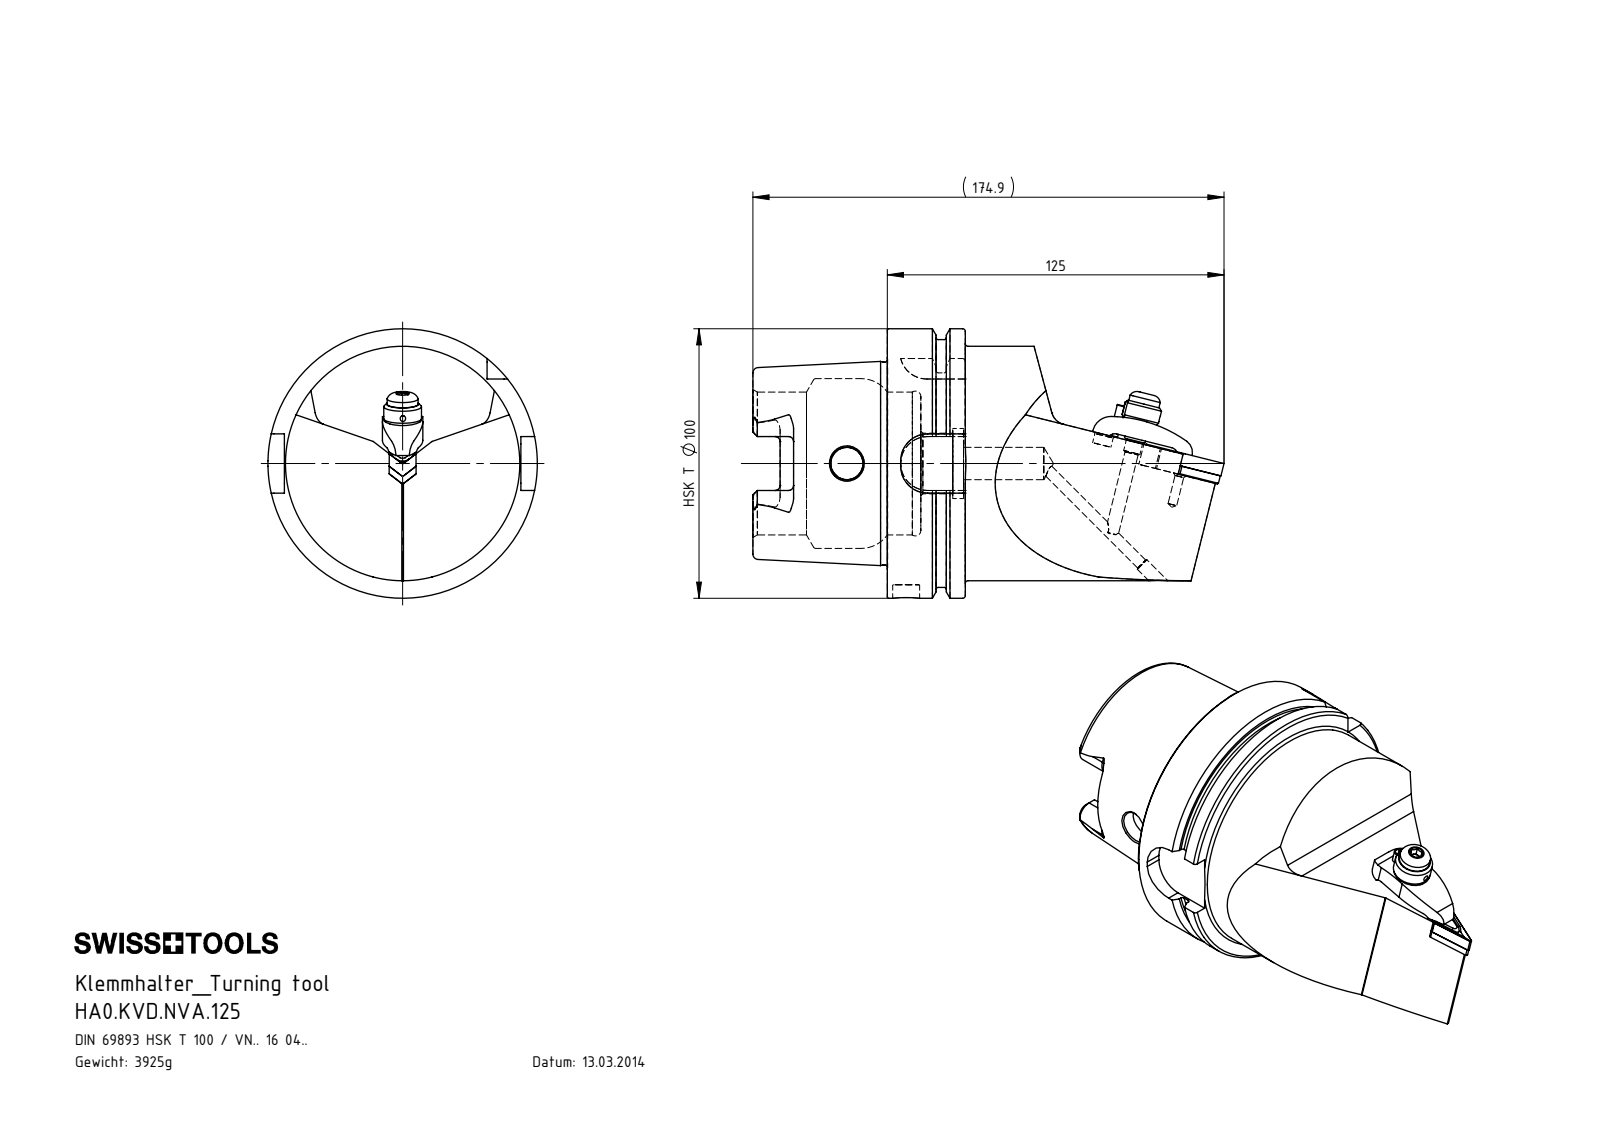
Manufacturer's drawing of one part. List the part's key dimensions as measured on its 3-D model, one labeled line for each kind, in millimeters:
Part name (STEP PRODUCT): HA0.KVD.NVA.125; ISO 13337 - 3 x 12_PreviewCfg; KVT_MB_600_050; WCC-ER3.102.029_C (+7 more)
STEP written by: SolidWorks 2017 (CONFIG_CONTROL_DESIGN)
Units: millimetres
Bodies: 12 solids, 465 faces (124 planar, 153 cylindrical, 188 other)
Overall size (bounding box): 174.9 × 100 × 100
Volume: 525 099 mm³ · Surface area: 72 201 mm²
Round holes (diameter × count): ⌀2 ×3, ⌀5 ×2, ⌀7 ×2, ⌀12 ×2, ⌀2.4 ×1, ⌀3 ×1, ⌀3.3 ×1, ⌀3.8 ×1, ⌀4 ×1, ⌀4.2 ×1, ⌀4.95 ×1, ⌀6.2 ×1
Round bosses / shafts (diameter × count): ⌀4 ×2, ⌀3 ×2, ⌀100 ×1, ⌀91.95 ×1, ⌀87 ×1, ⌀75.26 ×1, ⌀14 ×1, ⌀11.5 ×1
Partial cylindrical surfaces — rounded edges, fillets, slot ends (radius × count): R0.34 ×6, R0.59 ×6, R1.9 ×6, R0.4 ×4, R10 ×4, R1.5 ×3, R0.5 ×2, R0.8 ×2
Main face-to-face distances: 12.45, 28.95, 16.5, 49.9, 62.35, 78.85, 87.8, 78.2, 28.3, 15.85
Hole centre spacings: 27.32, 8.02, 19.31, 8.19, 19.13, 8.01, 19.3
